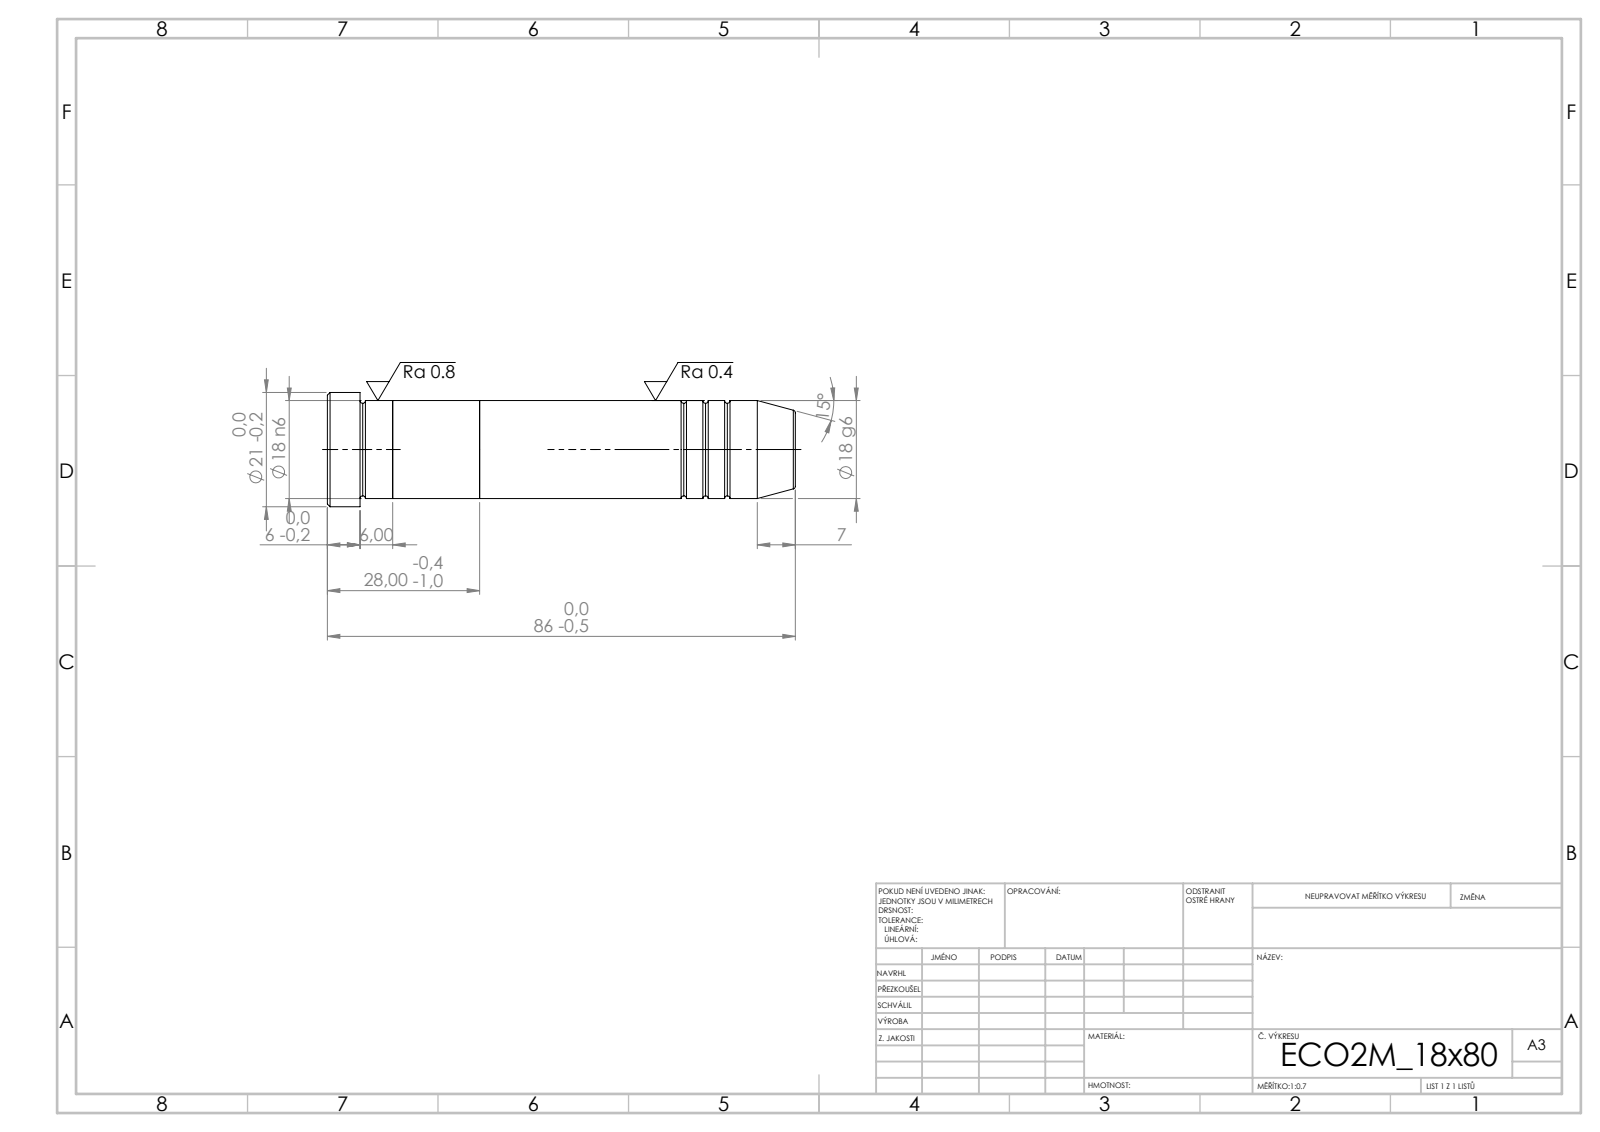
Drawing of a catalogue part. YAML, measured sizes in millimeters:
step_written_by: "SolidWorks 2019 (CONFIG_CONTROL_DESIGN)"
units: millimeters
bodies: {solids: 3, faces: 43, planar: 7, cylindrical: 14, other: 22}
overall_size: [86, 21, 21]
volume: 21994
surface_area: 6598
round_bosses_or_shafts:
  - {diameter: 21, count: 1}
  - {diameter: 18, count: 1}
face_to_face_distances: [16, 28, 12, 6, 58, 74, 86, 80, 22]
